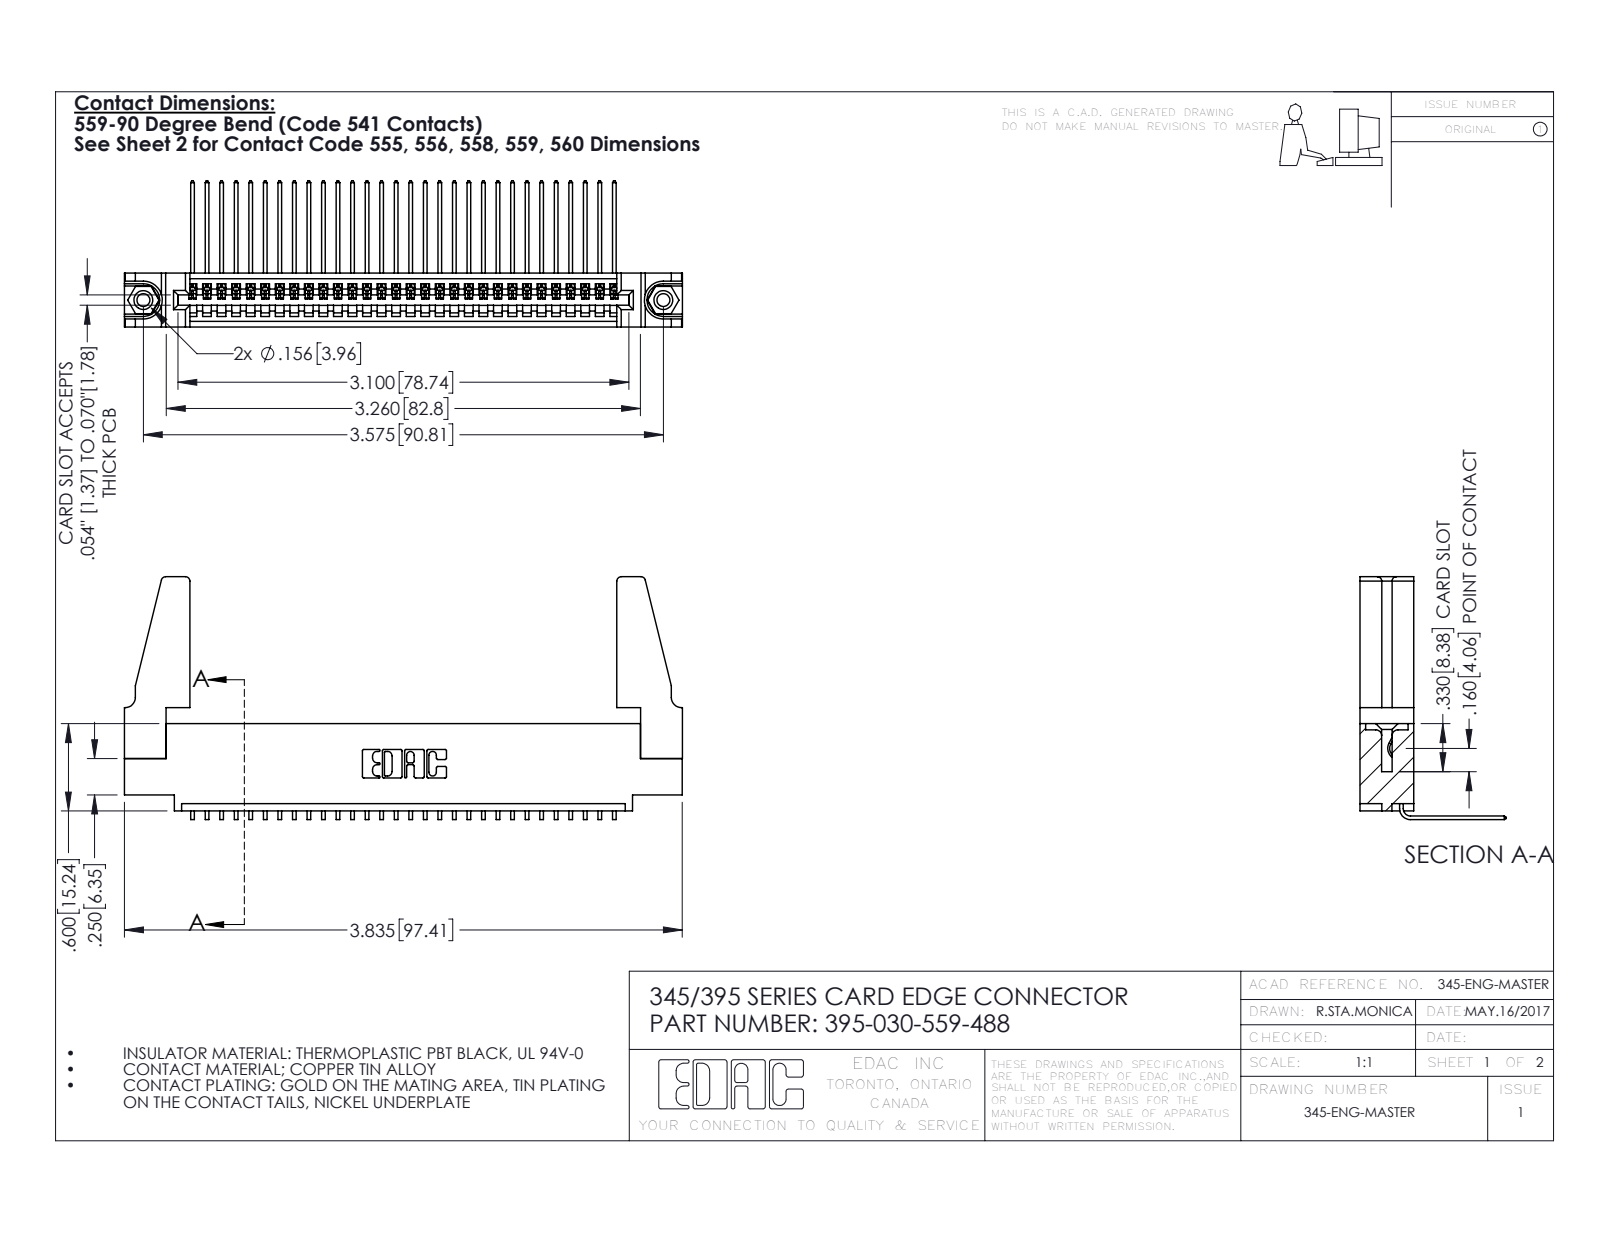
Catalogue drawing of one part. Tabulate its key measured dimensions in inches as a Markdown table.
| quantity | value |
| --- | --- |
| part name | 395-030-559-488; 345-250-001_345-250-001-102; 345 Part_0.110 Offset - 0.156 Dia-TH; 345-292-001_558 559 Tail - 1 (+1 more) |
| STEP written by | SolidWorks 2016 (CONFIG_CONTROL_DESIGN) |
| units | inches |
| bodies | 35 solids, 2054 faces (1416 planar, 622 cylindrical, 16 other) |
| overall size | 3.836 × 1.669 × 1.005 |
| volume | 0.759 in³ |
| surface area | 24.55 in² |
| round holes (diameter × count) | 0.089 × 2, 0.125 × 2, 0.156 × 2, 0.064 × 1 |
| round bosses / shafts (diameter × count) | 0.155 × 2 |
| partial cylindrical surfaces (radius × count) | 0.006 × 60, 0.01 × 22, 0.03 × 8, 0.007 × 6, 0.031 × 6, 0.026 × 3, 0.031 × 2, 0.04 × 2 |
| main face-to-face distances | 0.072, 0.37, 0.298, 0.2, 0.098, 0.272, 0.025, 0.225, 0.149, 0.072 |
| hole center spacings | 0.27, 3.34, 3.575 |
